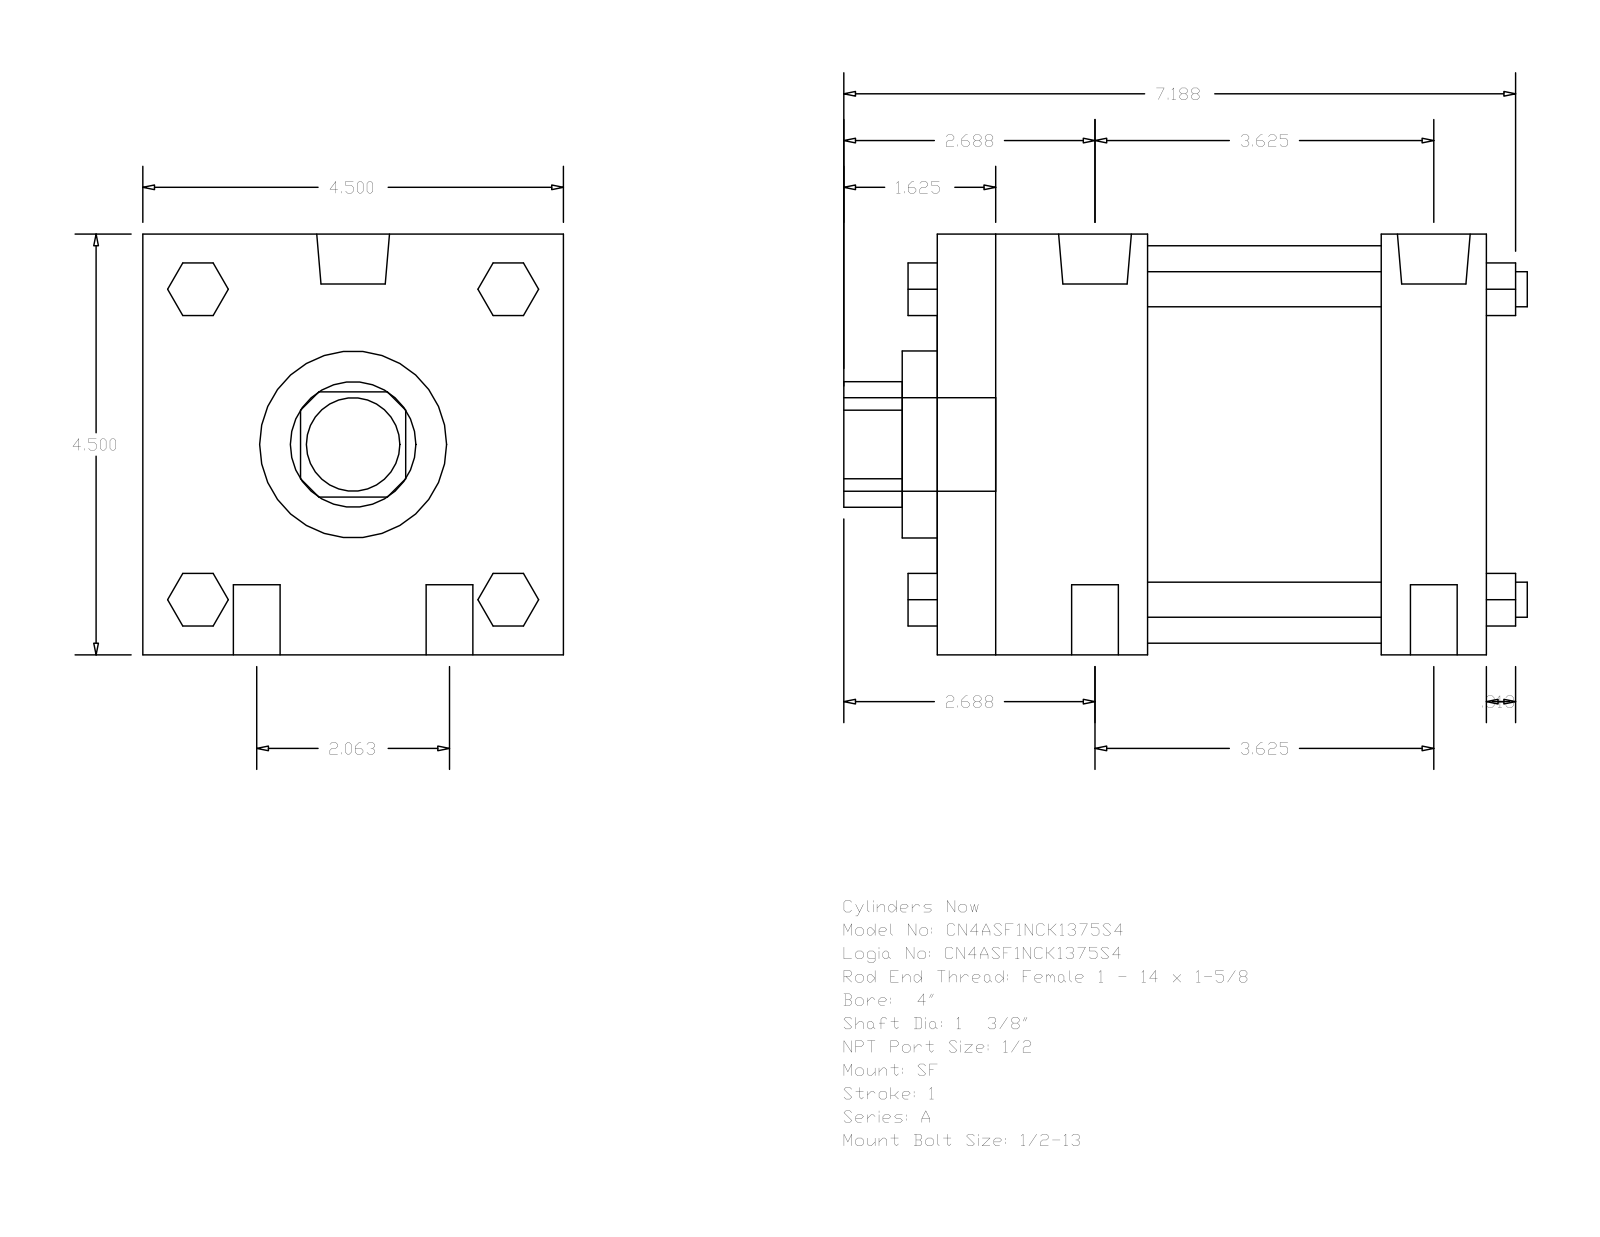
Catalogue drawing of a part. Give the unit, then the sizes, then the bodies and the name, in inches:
Units: inches
Overall size (bounding box): 7.313 × 4.5 × 4.5
Round holes (diameter × count): ⌀1.375 ×1, ⌀2 ×1, ⌀4.25 ×1
Round bosses / shafts (diameter × count): ⌀0.5 ×4, ⌀0.375 ×4, ⌀0.778 ×2, ⌀0.344 ×2, ⌀1 ×1
Partial cylindrical surfaces — rounded edges, fillets, slot ends (radius × count): R0.672 ×1
Main face-to-face distances: 4.5, 5.875, 1.125, 4.75, 2.25, 2.5, 3.625, 0.563, 0.375, 2.625
Bodies: 0 solids, 124 faces (94 planar, 30 cylindrical, 0 other)
Part name (STEP PRODUCT): A_SF__0400_1.375
STEP written by: GSSL Pune (CONFIG_CONTROL_DESIGN)
